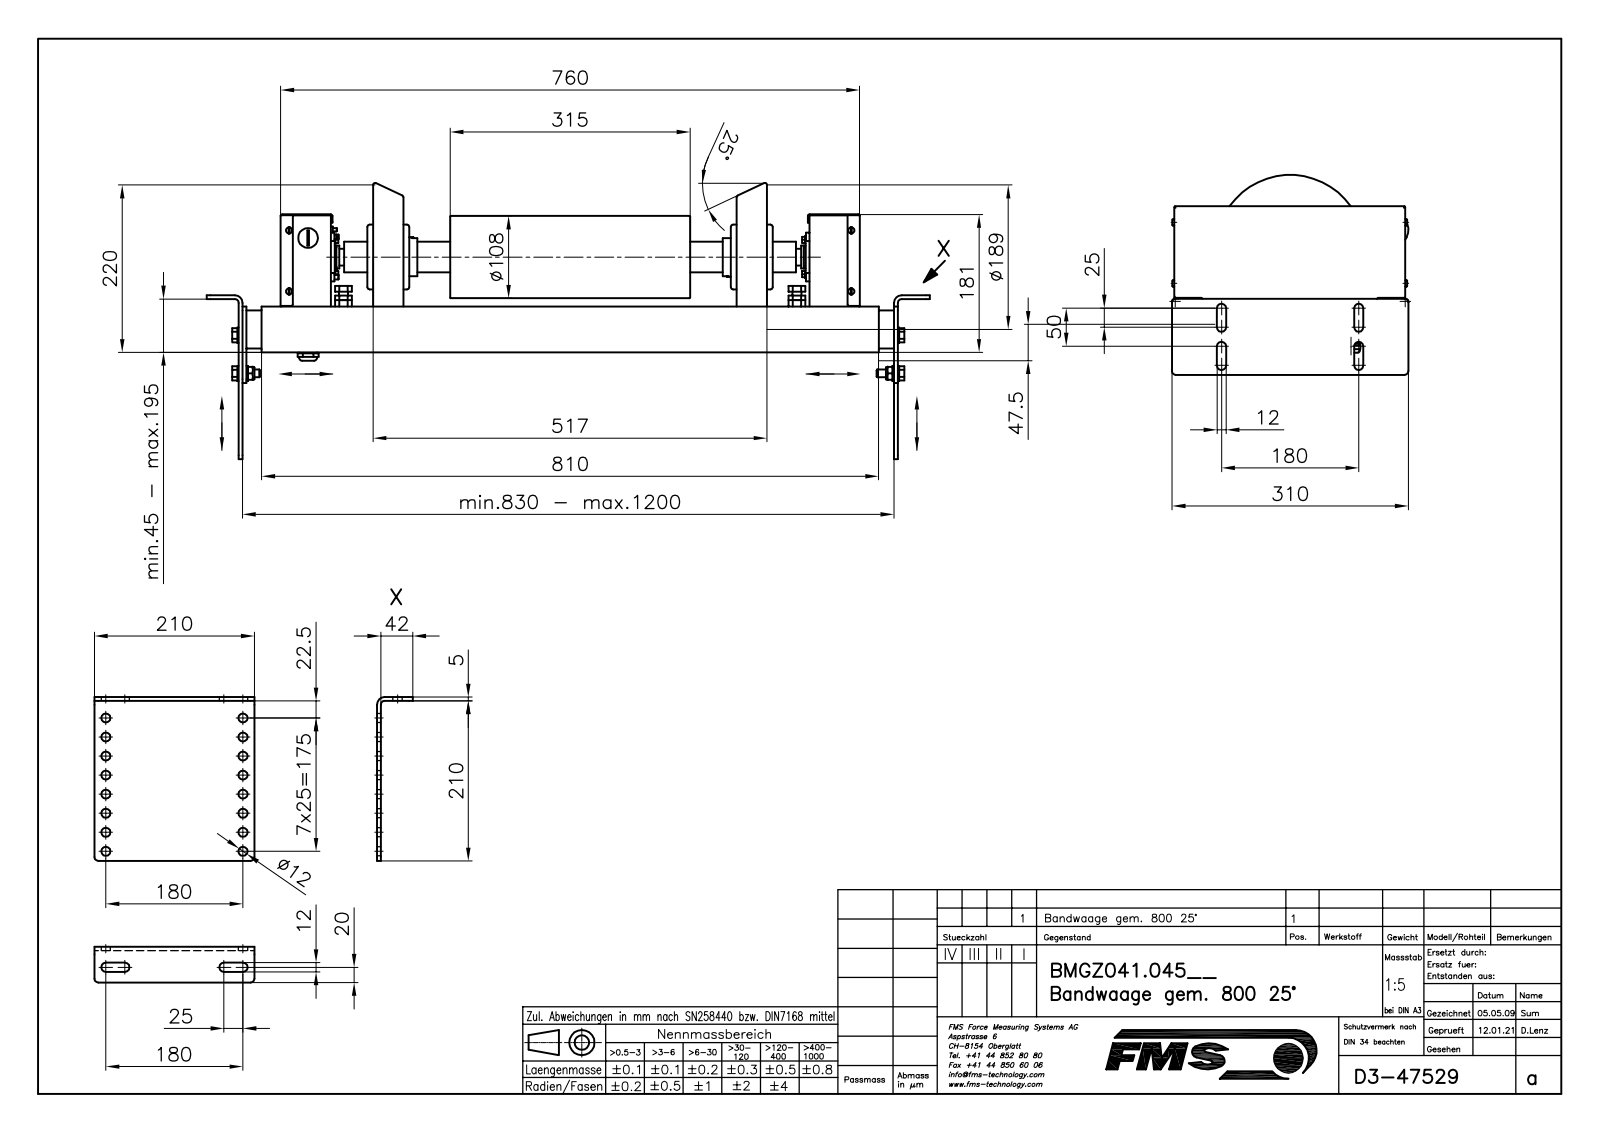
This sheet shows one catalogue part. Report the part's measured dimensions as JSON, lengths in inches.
{"part_name": "B47529_STP; B50030; 6KT-SCHRAUBE_M12X30; ZYL_SCHR__M4X8 (+8 more)", "step_written_by": "Mechanical Desktop 2009 (CONFIG_CONTROL_DESIGN)", "units": "inches", "bodies": {"solids": 156, "faces": 2658, "planar": 1351, "cylindrical": 944, "other": 363}, "overall_size": [37.362, 14.261, 12.213], "volume_in3": 476.9, "surface_area_in2": 4059, "round_holes": [[0.472, 17], [0.197, 6], [0.138, 4], [0.193, 4], [0.252, 4], [0.342, 4], [0.344, 4], [0.394, 4], [0.413, 4], [0.42, 4], [0.583, 4], [0.236, 3]], "round_bosses_or_shafts": [[0.472, 11], [0.323, 8], [0.165, 8], [0.787, 6], [0.394, 6], [0.197, 5], [0.63, 4], [0.437, 4]], "partial_cylinders_radius": [[0.079, 34], [0.039, 24], [0.157, 16], [0.197, 16], [0.236, 14], [0.138, 8], [0.089, 6], [0.02, 4]], "face_to_face_distances": [0.157, 0.197, 0.039, 2.008, 1.417, 10.63, 1.811, 1.969, 0.118, 2.205], "hole_center_spacings": [0.984, 7.155, 1.969, 7.355, 2.953, 7.677, 3.937, 7.087]}
